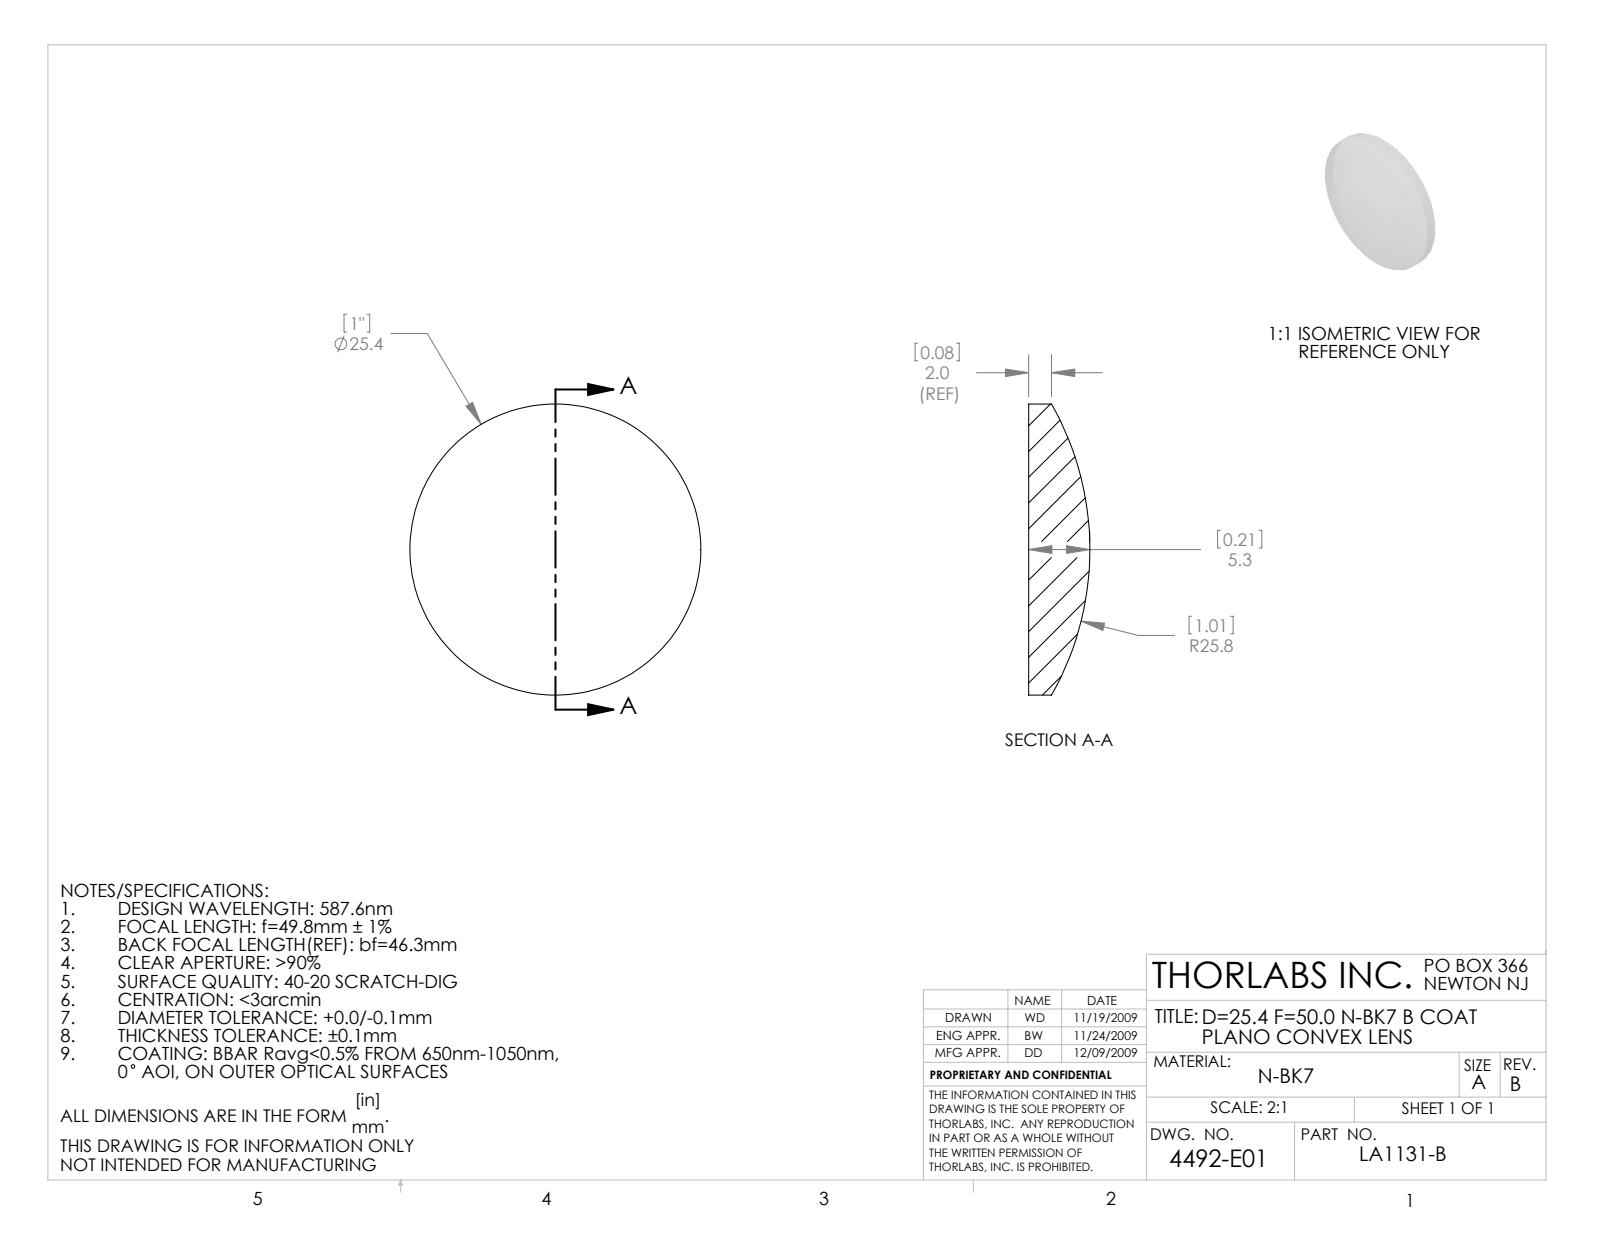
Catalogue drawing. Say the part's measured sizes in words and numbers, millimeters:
The part is named "4492-E0W". Its 3-D file was written by "SolidWorks 2009 (AUTOMOTIVE_DESIGN)". It is 1 solid with 5 faces: 1 planar, 2 cylindrical and 2 other. Overall it measures 25.4 by 25.4 by 5.34 millimeters. Its volume is 1 877 cubic millimeters and its surface area 1 207 square millimeters. Round bosses or shafts: 1 of diameter 25.4.
